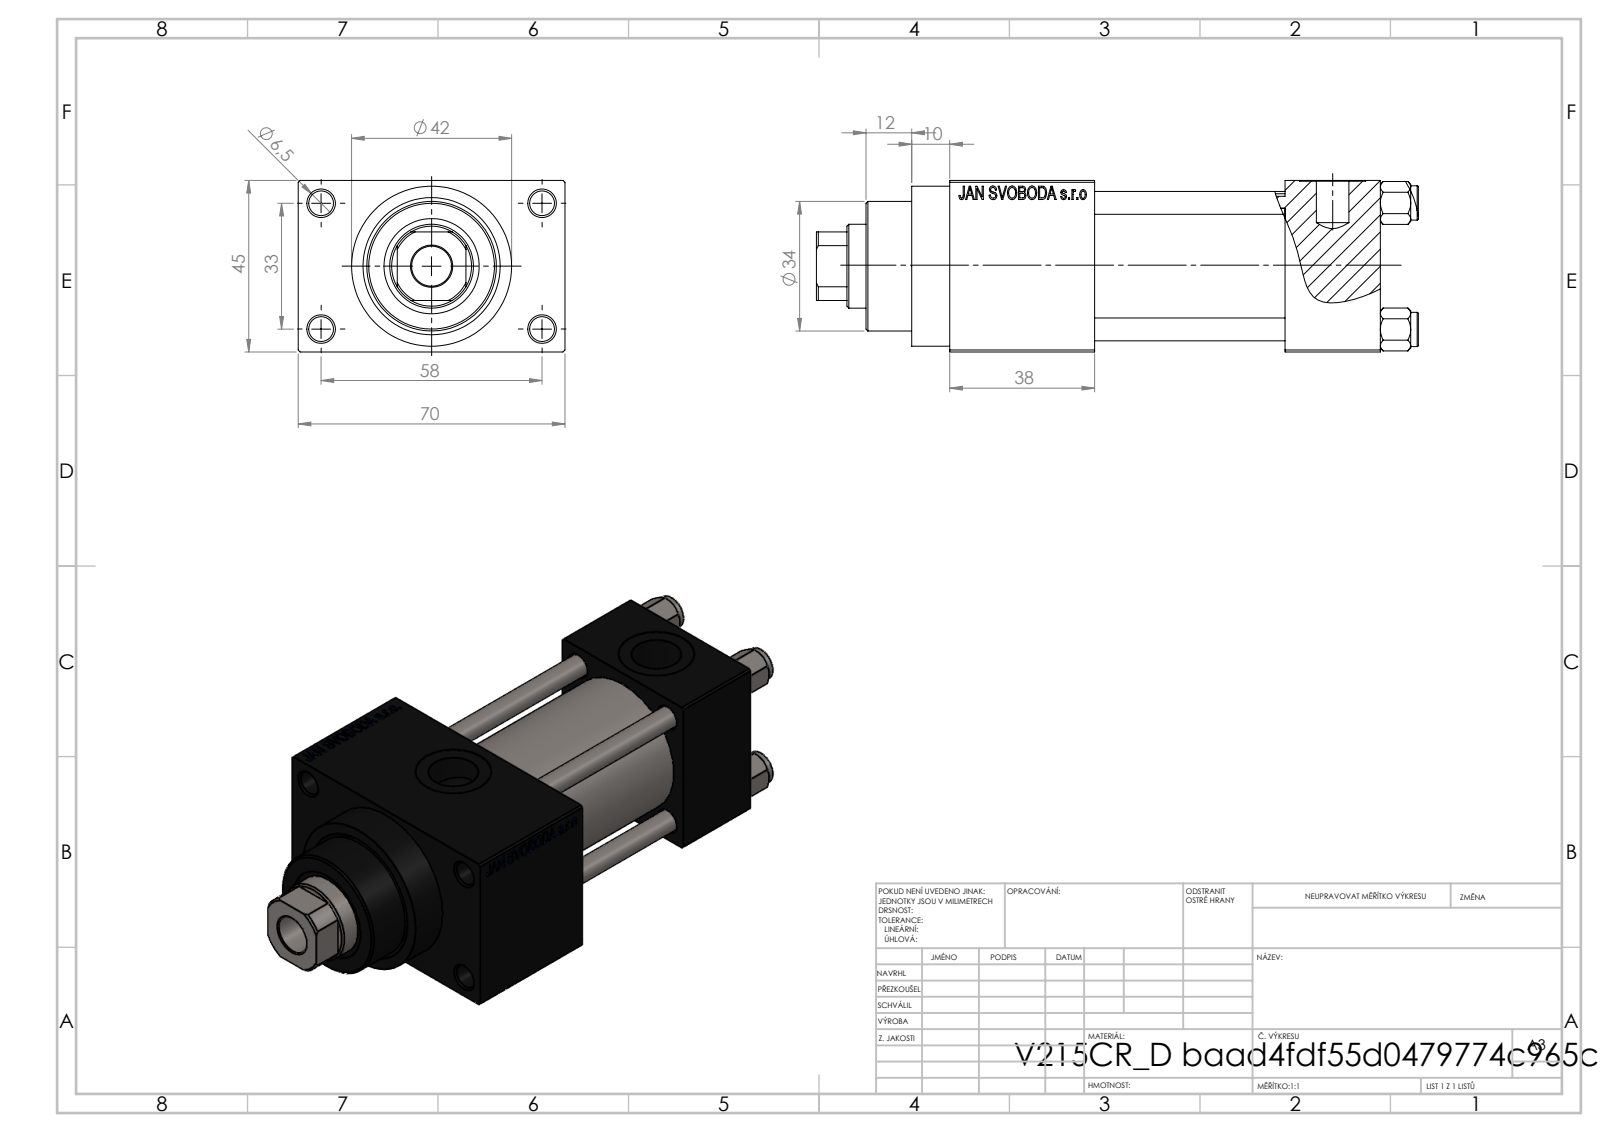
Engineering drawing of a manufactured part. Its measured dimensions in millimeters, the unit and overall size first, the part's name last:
Units: millimetres
Overall size (bounding box): 158 × 70 × 45
Round holes (diameter × count): ⌀6 ×4, ⌀6.5 ×4, ⌀7 ×2, ⌀13.16 ×2, ⌀20 ×2, ⌀10.5 ×1, ⌀22 ×1, ⌀24 ×1, ⌀25 ×1, ⌀32 ×1, ⌀33 ×1
Round bosses / shafts (diameter × count): ⌀9 ×4, ⌀42 ×1, ⌀38 ×1, ⌀34 ×1
Partial cylindrical surfaces — rounded edges, fillets, slot ends (radius × count): R10.5 ×1
Main face-to-face distances: 45, 25, 12.5, 57.5, 50, 75, 88, 70, 38, 113
Hole centre spacings: 12.4, 23.48, 33.2, 33.37, 35.35, 45.6, 56.35, 33
Volume: 244 496 mm³ · Surface area: 79 368 mm²
Bodies: 11 solids, 1105 faces (496 planar, 89 cylindrical, 520 other)
Part name (STEP PRODUCT): V215_VC_A; V215CR_VCP_D; V215CR_D_Body; NUT_M5_D (+1 more)
STEP written by: SolidWorks 2019 (CONFIG_CONTROL_DESIGN)
